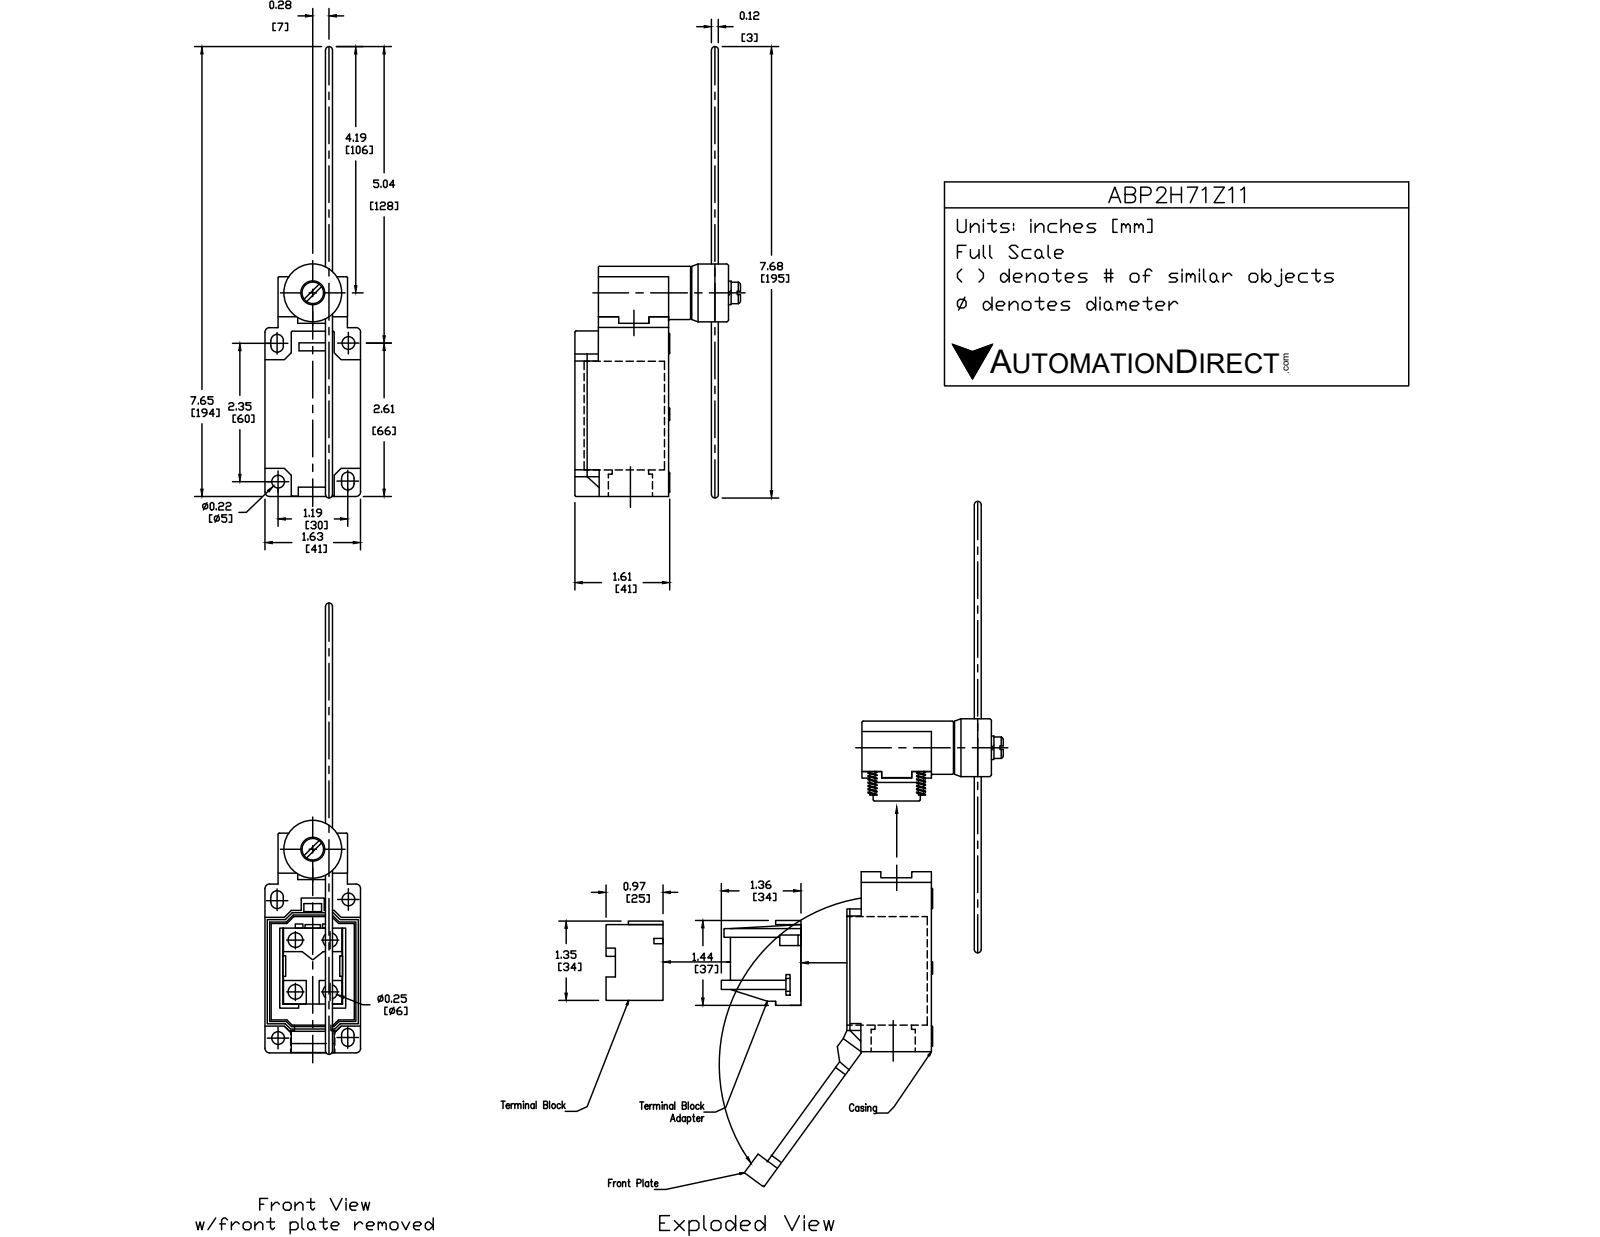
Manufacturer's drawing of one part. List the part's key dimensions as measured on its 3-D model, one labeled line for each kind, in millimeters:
Part name (STEP PRODUCT): ABP2H71Z11
STEP written by: SolidWorks 2017 (AUTOMOTIVE_DESIGN)
Units: millimetres
Bodies: 7 solids, 219 faces (122 planar, 79 cylindrical, 18 other)
Overall size (bounding box): 194.9 × 61.3 × 41
Volume: 141 400 mm³ · Surface area: 29 040 mm²
Round holes (diameter × count): ⌀5.4 ×2, ⌀6 ×1, ⌀14 ×1, ⌀17 ×1, ⌀19 ×1
Round bosses / shafts (diameter × count): ⌀9 ×5, ⌀25 ×1, ⌀23 ×1, ⌀18 ×1, ⌀10 ×1, ⌀3 ×1
Partial cylindrical surfaces — rounded edges, fillets, slot ends (radius × count): R0.5 ×16, R2 ×4, R2.7 ×4, R11.5 ×1, R12 ×1
Main face-to-face distances: 41, 39.8, 30, 5.5, 35.5, 75.5, 9.8, 2.5, 78, 15.8
Hole centre spacings: 26.5, 35, 67.1, 83.2
